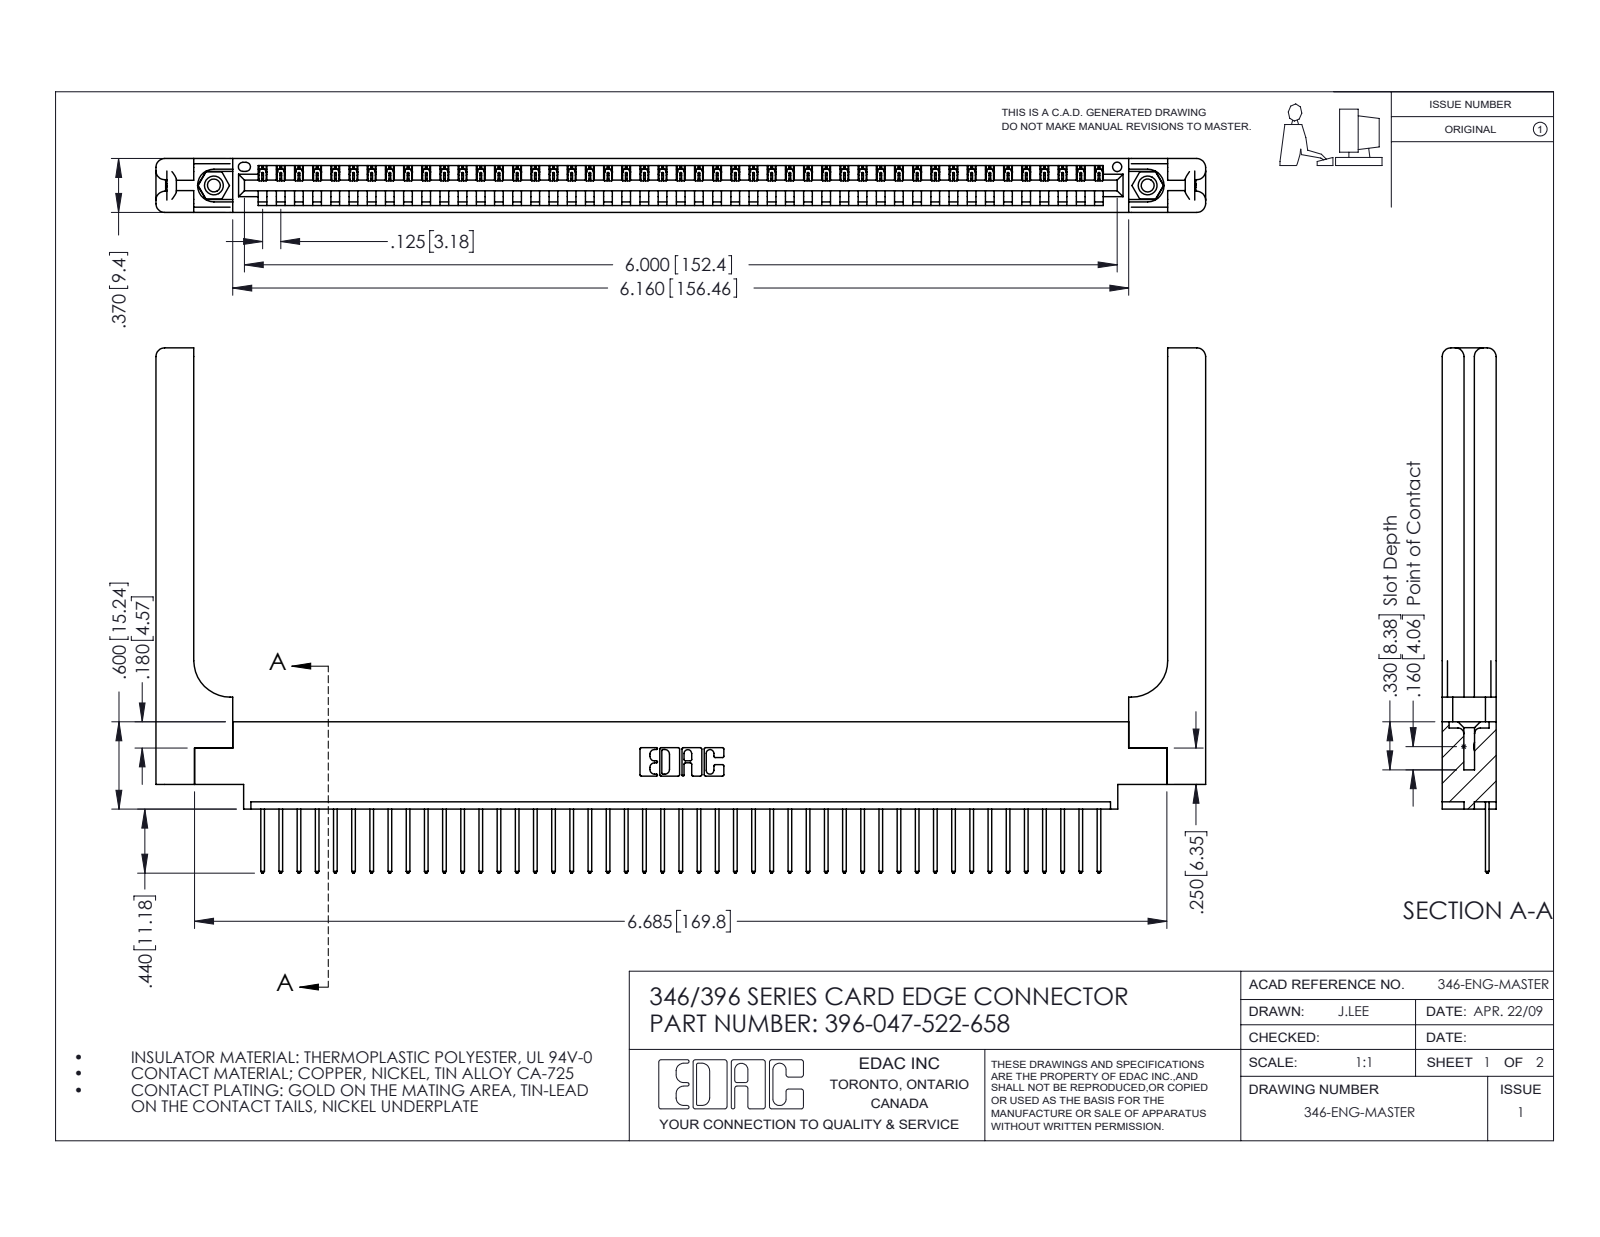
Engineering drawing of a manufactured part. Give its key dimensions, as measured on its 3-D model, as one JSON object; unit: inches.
{"part_name": "346-220-058_345-220-058; 346 Part_0.170 Offset - 0.156 Dia-TH; 396-047-522-658; 345-292-001_345-293-122 (+1 more)", "step_written_by": "SolidWorks 2016 (CONFIG_CONTROL_DESIGN)", "units": "inches", "bodies": {"solids": 52, "faces": 3108, "planar": 2108, "cylindrical": 940, "other": 60}, "overall_size": [7.216, 3.61, 0.37], "volume_in3": 1.522, "surface_area_in2": 42.38, "round_holes": [[0.089, 2], [0.125, 2], [0.156, 2], [0.064, 1]], "round_bosses_or_shafts": [[0.155, 2]], "partial_cylinders_radius": [[0.006, 94], [0.01, 94], [0.01, 22], [0.06, 16], [0.007, 6], [0.031, 6], [0.026, 3], [0.03, 2]], "face_to_face_distances": [0.37, 0.048, 0.322, 0.072, 0.148, 0.15, 0.25, 0.298, 0.025, 0.222], "hole_center_spacings": [0.246, 6.211, 6.42]}
